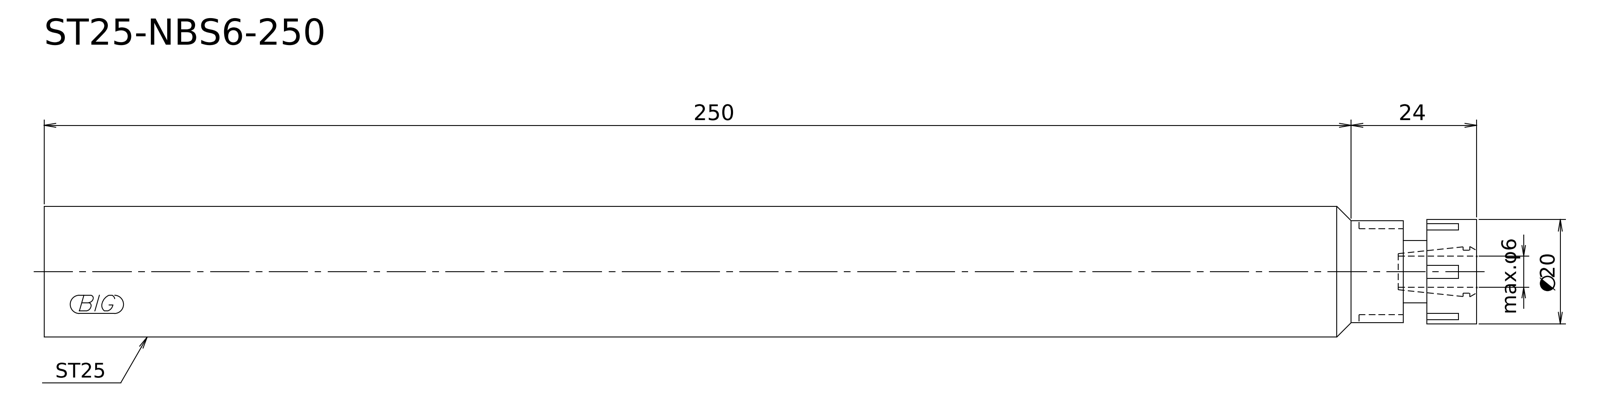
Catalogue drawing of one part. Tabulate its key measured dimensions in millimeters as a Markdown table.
| quantity | value |
| --- | --- |
| STEP written by | Kubotek KeyCreator V8.5.1 (14335) (CONFIG_CONTROL_DESIGN) |
| units | millimeters |
| bodies | 1 solid, 9 faces (4 planar, 4 cylindrical, 1 other) |
| overall size | 274 × 25 × 25 |
| volume | 128 923 mm³ |
| surface area | 22 262 mm² |
| round bosses / shafts (diameter × count) | 25 × 1, 20 × 1, 19.5 × 1, 12 × 1 |
| main face-to-face distances | 274, 9.5, 264.5, 14, 4.5, 260 |
